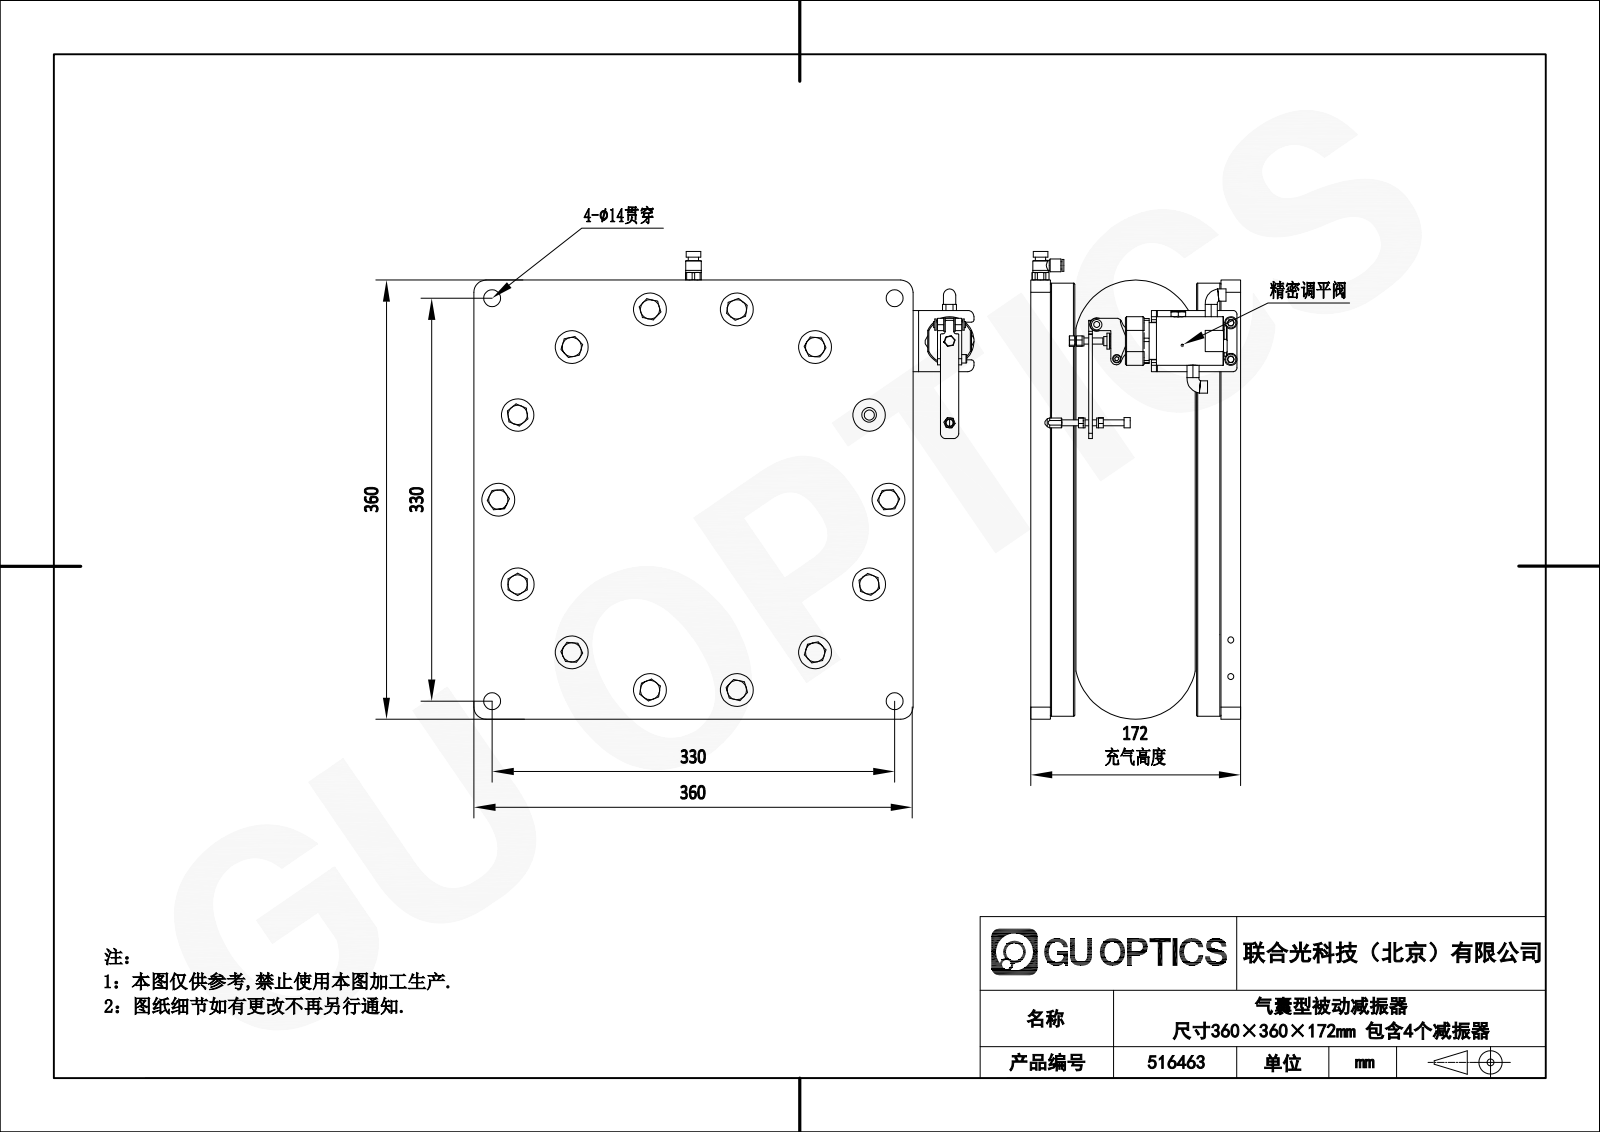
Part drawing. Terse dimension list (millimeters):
name: 516463
written by: SolidWorks 2020 (CONFIG_CONTROL_DESIGN)
unit: mm
bodies: 0 solids, 732 faces (402 planar, 149 cylindrical, 181 other)
size: 410 × 383.5 × 172
holes: 14× ⌀27, 4× ⌀14, 3× ⌀5, 1× ⌀9, 1× ⌀9.7, 1× ⌀11, 1× ⌀11.5, 1× ⌀12.7, 1× ⌀13, 1× ⌀40, 1× ⌀355
bosses: 15× ⌀8.5, 3× ⌀10, 3× ⌀8, 2× ⌀7, 2× ⌀5, 1× ⌀30, 1× ⌀12.6, 1× ⌀12
rounds: 6× R5, 4× R2, 4× R10, 3× R0.3, 2× R3, 2× R4.5, 1× R4.74, 1× R7
face distances: 16, 156, 140, 172, 20, 36, 136, 120, 100, 360
hole spacings: 288.31, 138.84, 199.52, 71.21, 160, 250.19, 311.97, 250.18
